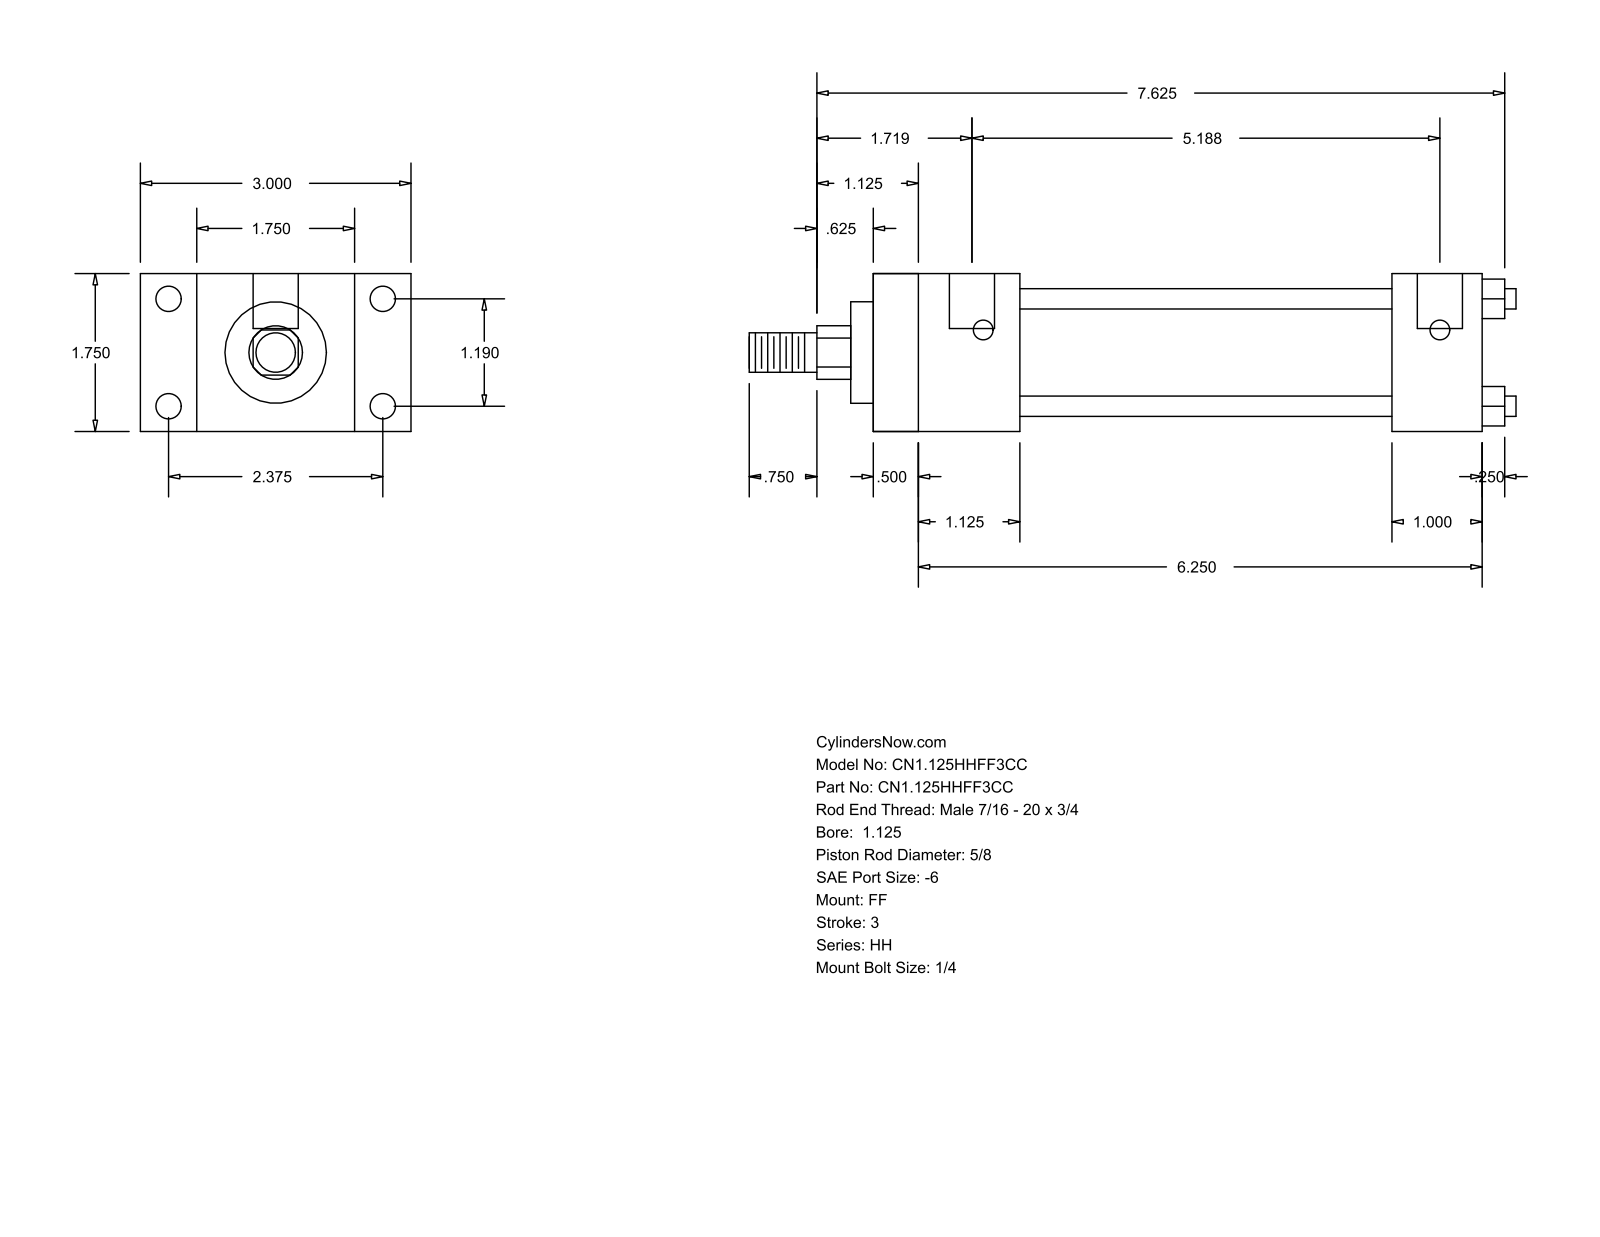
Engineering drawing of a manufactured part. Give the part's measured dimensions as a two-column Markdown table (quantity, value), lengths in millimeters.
| quantity | value |
| --- | --- |
| part name | HH_FF__0112_0.625 |
| STEP written by | GSSL Pune (CONFIG_CONTROL_DESIGN) |
| units | millimeters |
| bodies | 0 solids, 92 faces (64 planar, 28 cylindrical, 0 other) |
| overall size | 215.9 × 76.2 × 44.45 |
| round holes (diameter × count) | 5.56 × 4, 7.14 × 4, 12.7 × 2 |
| round bosses / shafts (diameter × count) | 5.71 × 4, 34.92 × 1, 28.57 × 1, 15.88 × 1, 11.11 × 1 |
| partial cylindrical surfaces (radius × count) | 7.54 × 1 |
| main face-to-face distances | 44.46, 171.44, 12.69, 158.75, 15.87, 28.58, 60.33, 41.27, 146.05, 133.36 |
| hole center spacings | 30.22, 60.32, 67.47, 128.59, 3.17, 131.76 |
